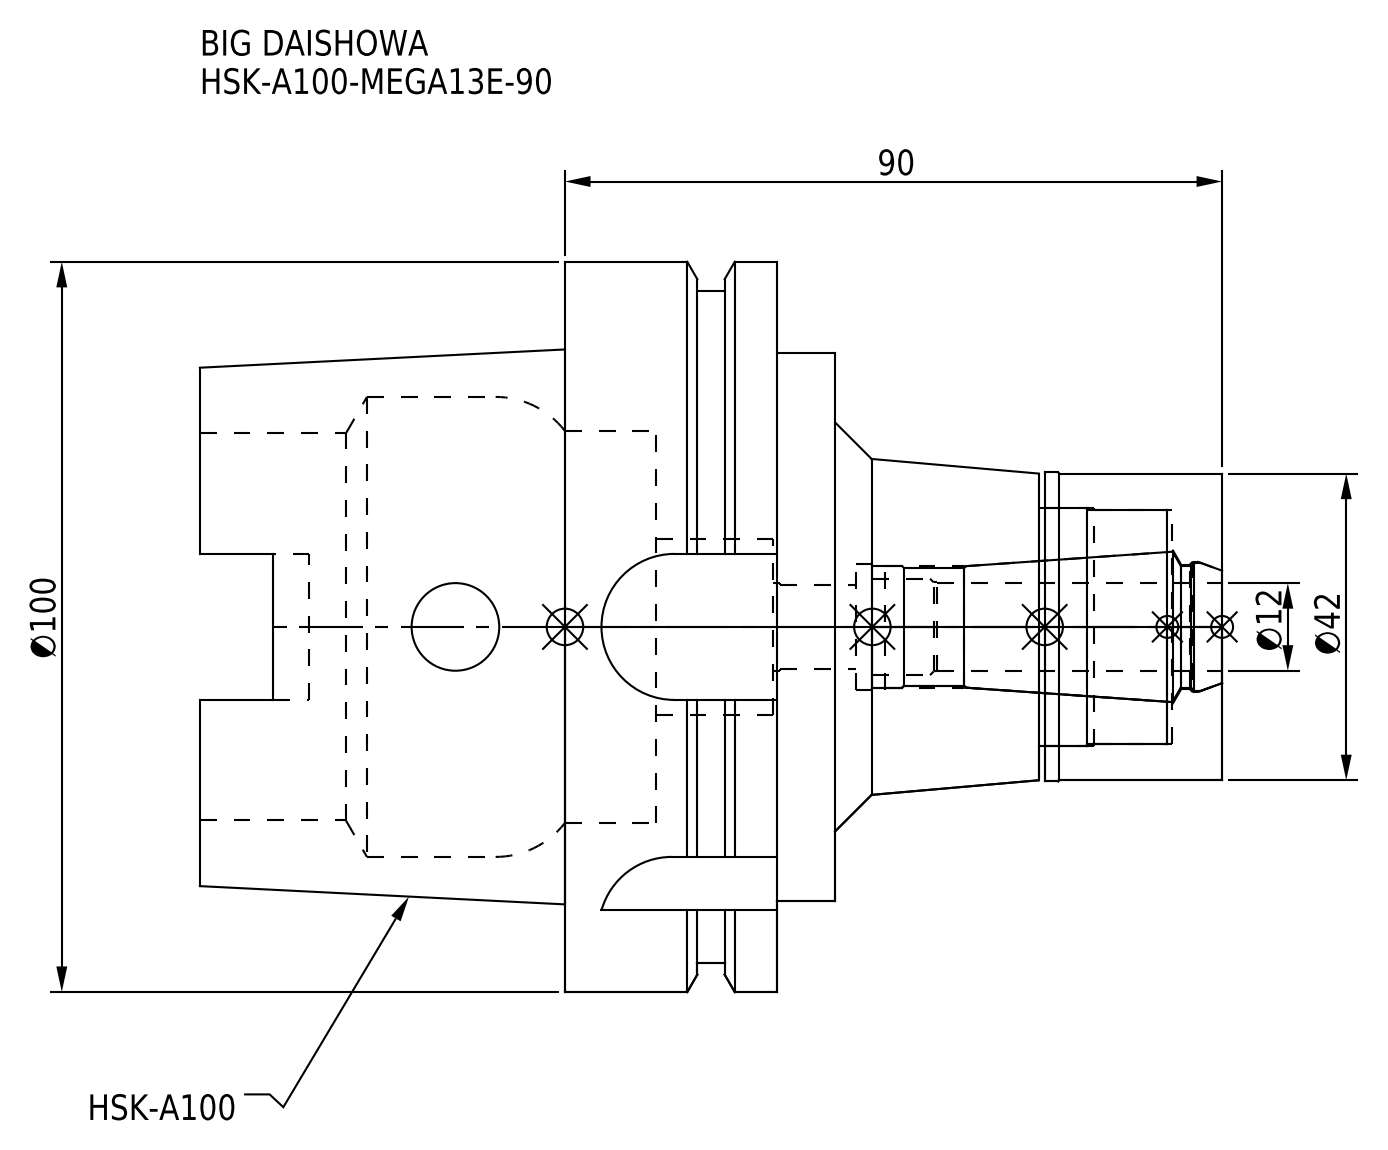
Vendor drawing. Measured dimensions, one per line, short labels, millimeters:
name: HSK-A100-MEGA13E-90-120-FreeParts; DXF_TEMP_ASSY_ASM_4_ASM.stp; HSK-A100-MEGA13E-90; MEN13_1.stp (+3 more)
written by: SolidWorks 2019 (CONFIG_CONTROL_DESIGN)
unit: mm
bodies: 2 solids, 126 faces (42 planar, 56 cylindrical, 28 other)
size: 140 × 100 × 100
volume: 354 235 mm³; area: 67 132 mm²
holes: 2× ⌀12, 1× ⌀11.5, 1× ⌀16.6, 1× ⌀17, 1× ⌀17.2, 1× ⌀17.9, 1× ⌀24, 1× ⌀32, 1× ⌀32.5, 1× ⌀53, 1× ⌀53.8, 1× ⌀63
bosses: 1× ⌀100, 1× ⌀92, 1× ⌀75, 1× ⌀42.3, 1× ⌀42
rounds: 4× R4.88, 4× R10
face distances: 29, 8, 37, 24.55, 16.55, 12.45, 53, 61, 77.55, 90
